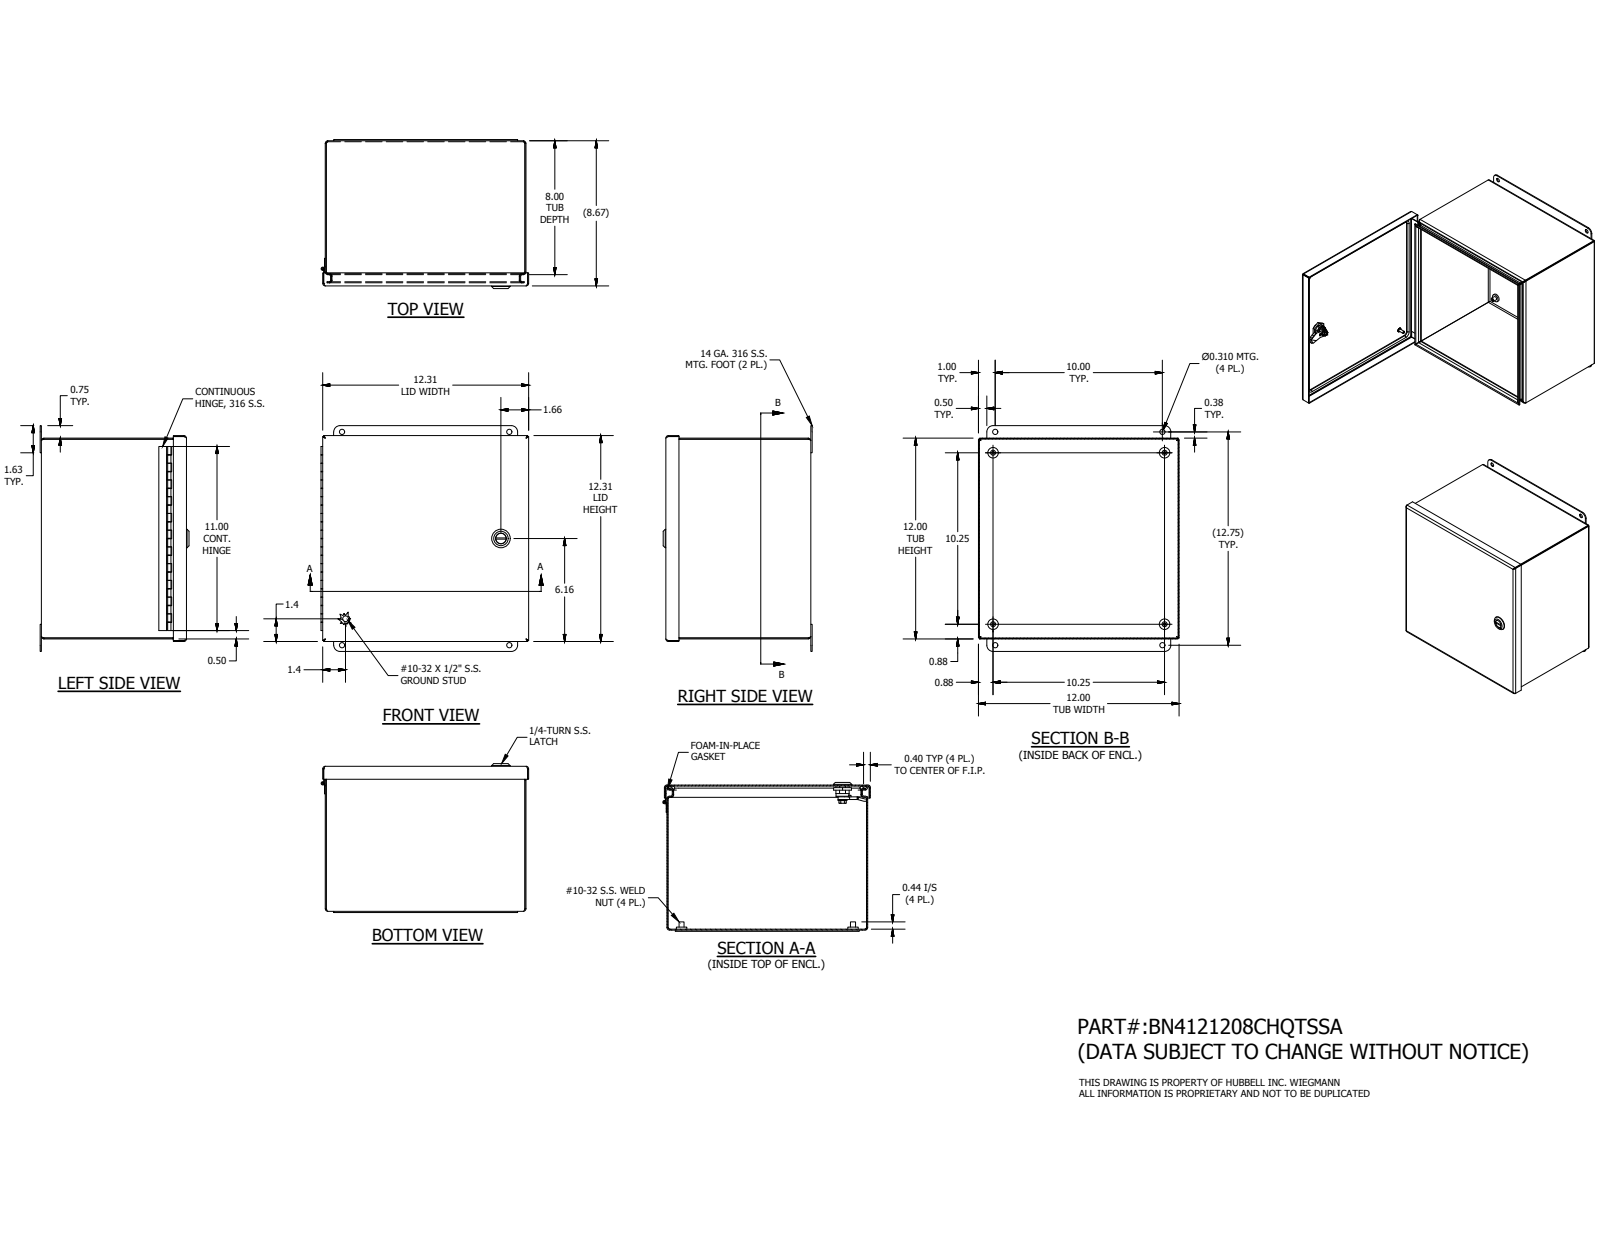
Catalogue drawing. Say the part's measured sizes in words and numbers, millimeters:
The part is named "BN41212CHQTSSALID; 12x12; 348131; 32884LH (+8 more)". Its 3-D file was written by "Autodesk Inventor 2016 (AUTOMOTIVE_DESIGN)". It is 21 solids with 671 faces: 366 planar, 208 cylindrical and 97 other. Overall it measures 342.9 by 315.26 by 226.19 millimeters. Its volume is 860 161 cubic millimeters and its surface area 1 088 000 square millimeters. Round holes: 4 of diameter 3.96, 4 of diameter 7.87, 1 of diameter 2.96, 1 of diameter 5, 1 of diameter 8, 1 of diameter 10, 1 of diameter 10.2, 1 of diameter 16.1, 1 of diameter 20.38. Round bosses or shafts: 4 of diameter 15.88, 4 of diameter 7.62, 1 of diameter 28, 1 of diameter 19.8, 1 of diameter 16, 1 of diameter 15.2, 1 of diameter 13.5, 1 of diameter 12.8. Partial cylindrical surfaces (rounded edges, fillets, slot ends): 20 of radius 2.38, 20 of radius 3.88, 16 of radius 3.17, 8 of radius 0.5, 4 of radius 4, 4 of radius 9.53, 2 of radius 2.31, 1 of radius 6.45. The main face-to-face distances are 1.5, 303.3, 1.49, 304.8, 218.79, 220.28, 217.29, 218.78, 303.31, 301.81. The hole center spacings are 31.91, 260.35, 292.12, 389.18, 131.14, 254, 259.12, 259.13.
